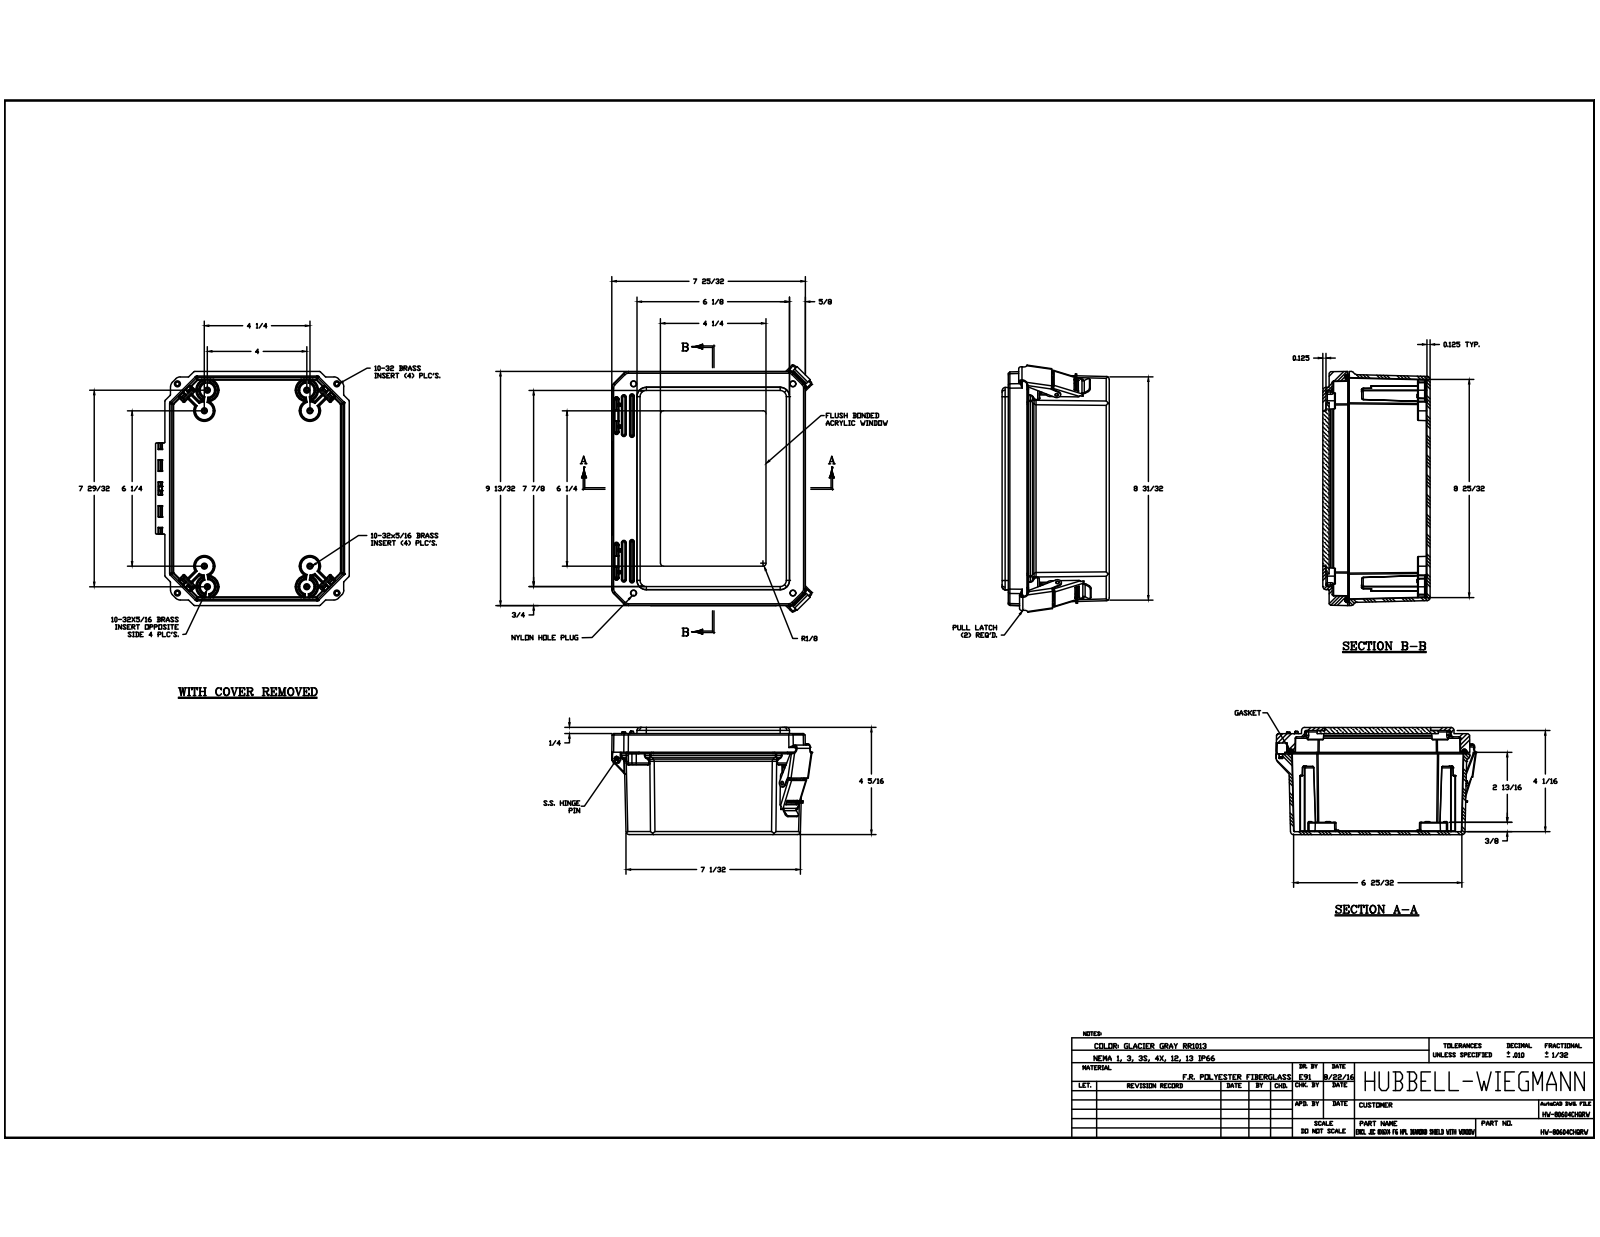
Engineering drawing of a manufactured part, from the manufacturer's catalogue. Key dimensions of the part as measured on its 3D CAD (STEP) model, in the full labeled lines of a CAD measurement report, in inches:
Part name (STEP PRODUCT): DSW80604HPL_STP; DS080604BOX; BRASS INSERT-(; BRASS INSERT-(_1 (+8 more)
STEP written by: Autodesk Inventor 2017 (AUTOMOTIVE_DESIGN)
Units: inches
Bodies: 34 solids, 2175 faces (772 planar, 855 cylindrical, 548 other)
Overall size (bounding box): 10.046 × 8.107 × 4.312
Volume: 48.14 in³ · Surface area: 650.4 in²
Round holes (diameter × count): ⌀0.156 ×16, ⌀0.152 ×8, ⌀0.135 ×6, ⌀0.15 ×4, ⌀0.252 ×4, ⌀0.253 ×4, ⌀0.135 ×2, ⌀0.219 ×2, ⌀0.227 ×2, ⌀0.313 ×2, ⌀0.375 ×2, ⌀0.137 ×1
Round bosses / shafts (diameter × count): ⌀0.246 ×16, ⌀0.87 ×4, ⌀0.3 ×4, ⌀0.209 ×4, ⌀0.435 ×2, ⌀0.135 ×2
Partial cylindrical surfaces — rounded edges, fillets, slot ends (radius × count): R0.01 ×104, R0.005 ×80, R0.02 ×65, R0.03 ×61, R0.06 ×33, R0.063 ×27, R0.09 ×26, R0.125 ×26
Main face-to-face distances: 0.125, 0.125, 4.06, 0.25, 4.087, 3.962, 0.124, 4.312, 4.187, 0.225
Hole centre spacings: 7.411, 9.065, 8.193, 0.837, 4.25, 7.08, 7.558, 8.249
